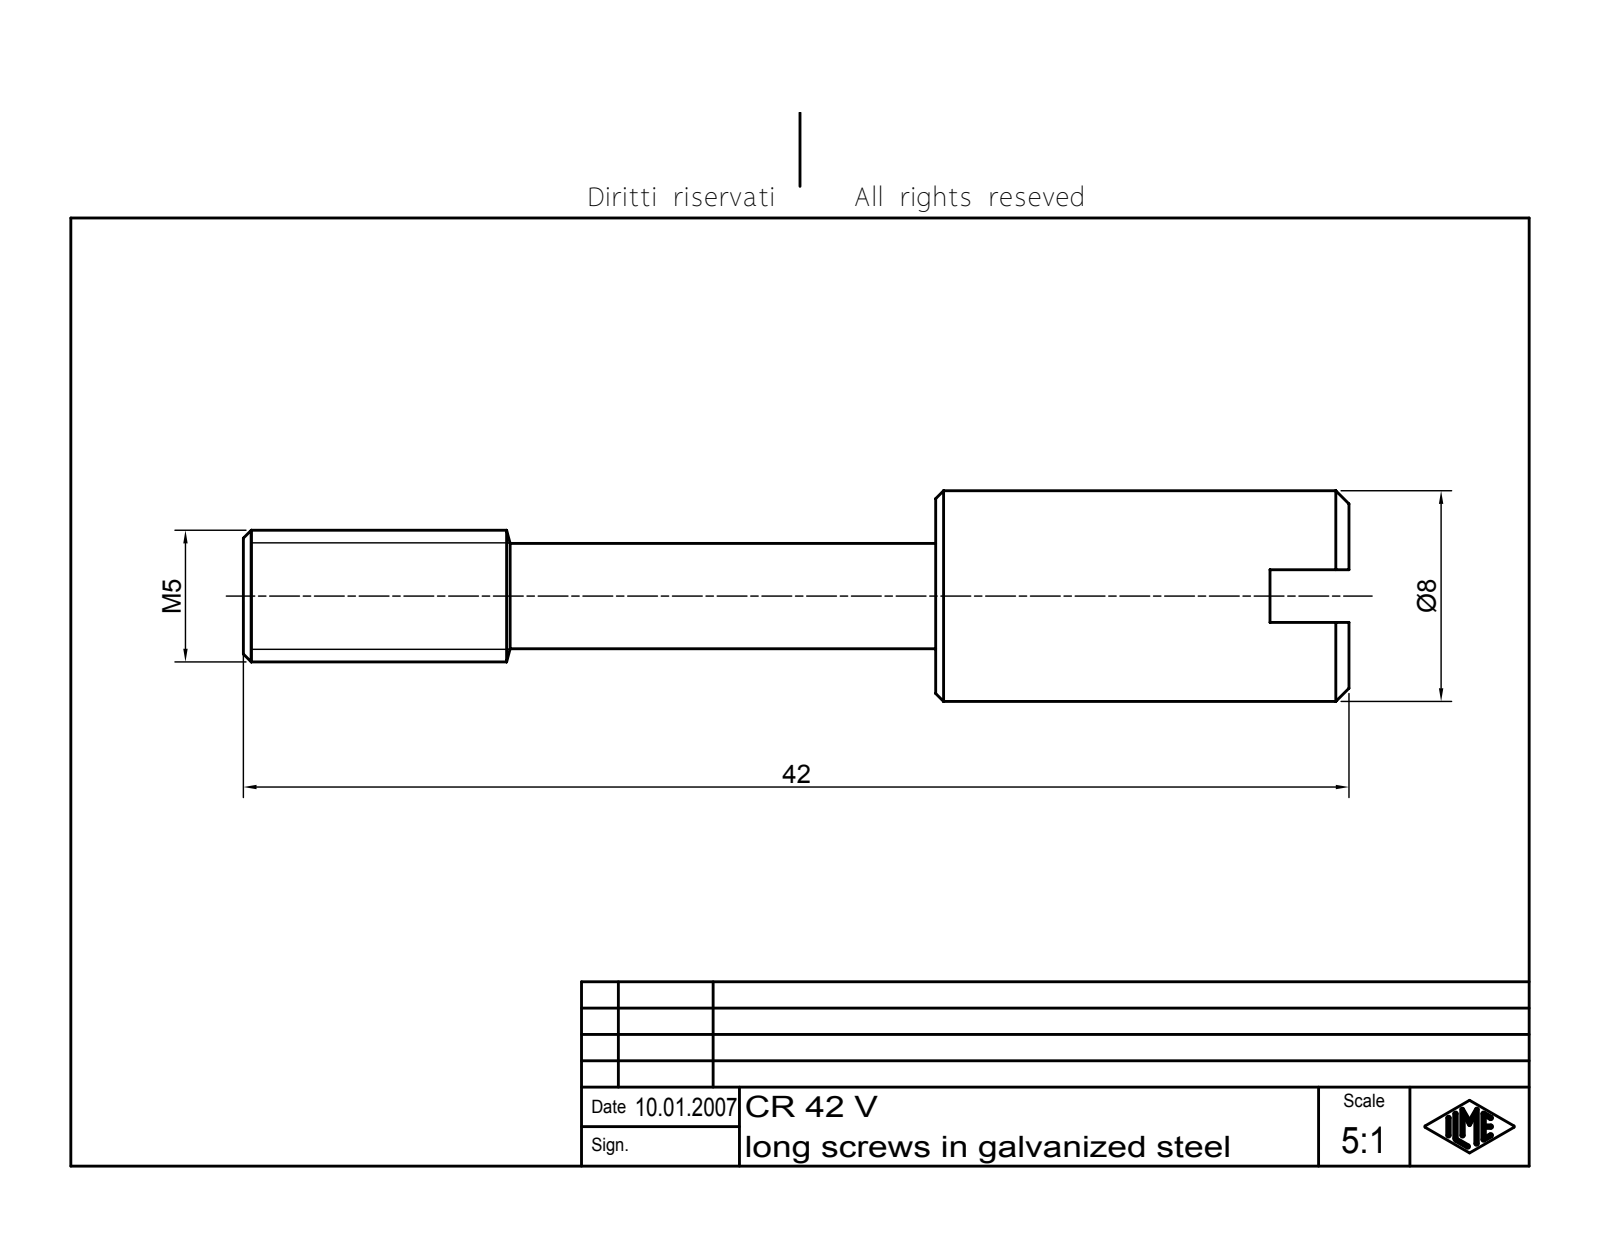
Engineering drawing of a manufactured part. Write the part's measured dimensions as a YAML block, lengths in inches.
part_name: "CR 42 V"
step_written_by: "Autodesk Inventor 7 (AUTOMOTIVE_DESIGN)"
units: inches
bodies: {solids: 1, faces: 21, planar: 7, cylindrical: 6, other: 8}
overall_size: [1.654, 0.315, 0.315]
volume: 0.07
surface_area: 1.38
round_bosses_or_shafts:
  - {diameter: 0.315, count: 1}
  - {diameter: 0.197, count: 1}
  - {diameter: 0.157, count: 1}
face_to_face_distances: [0.618, 0.079, 0.5, 0.118, 1.035, 1.535, 1.654]
